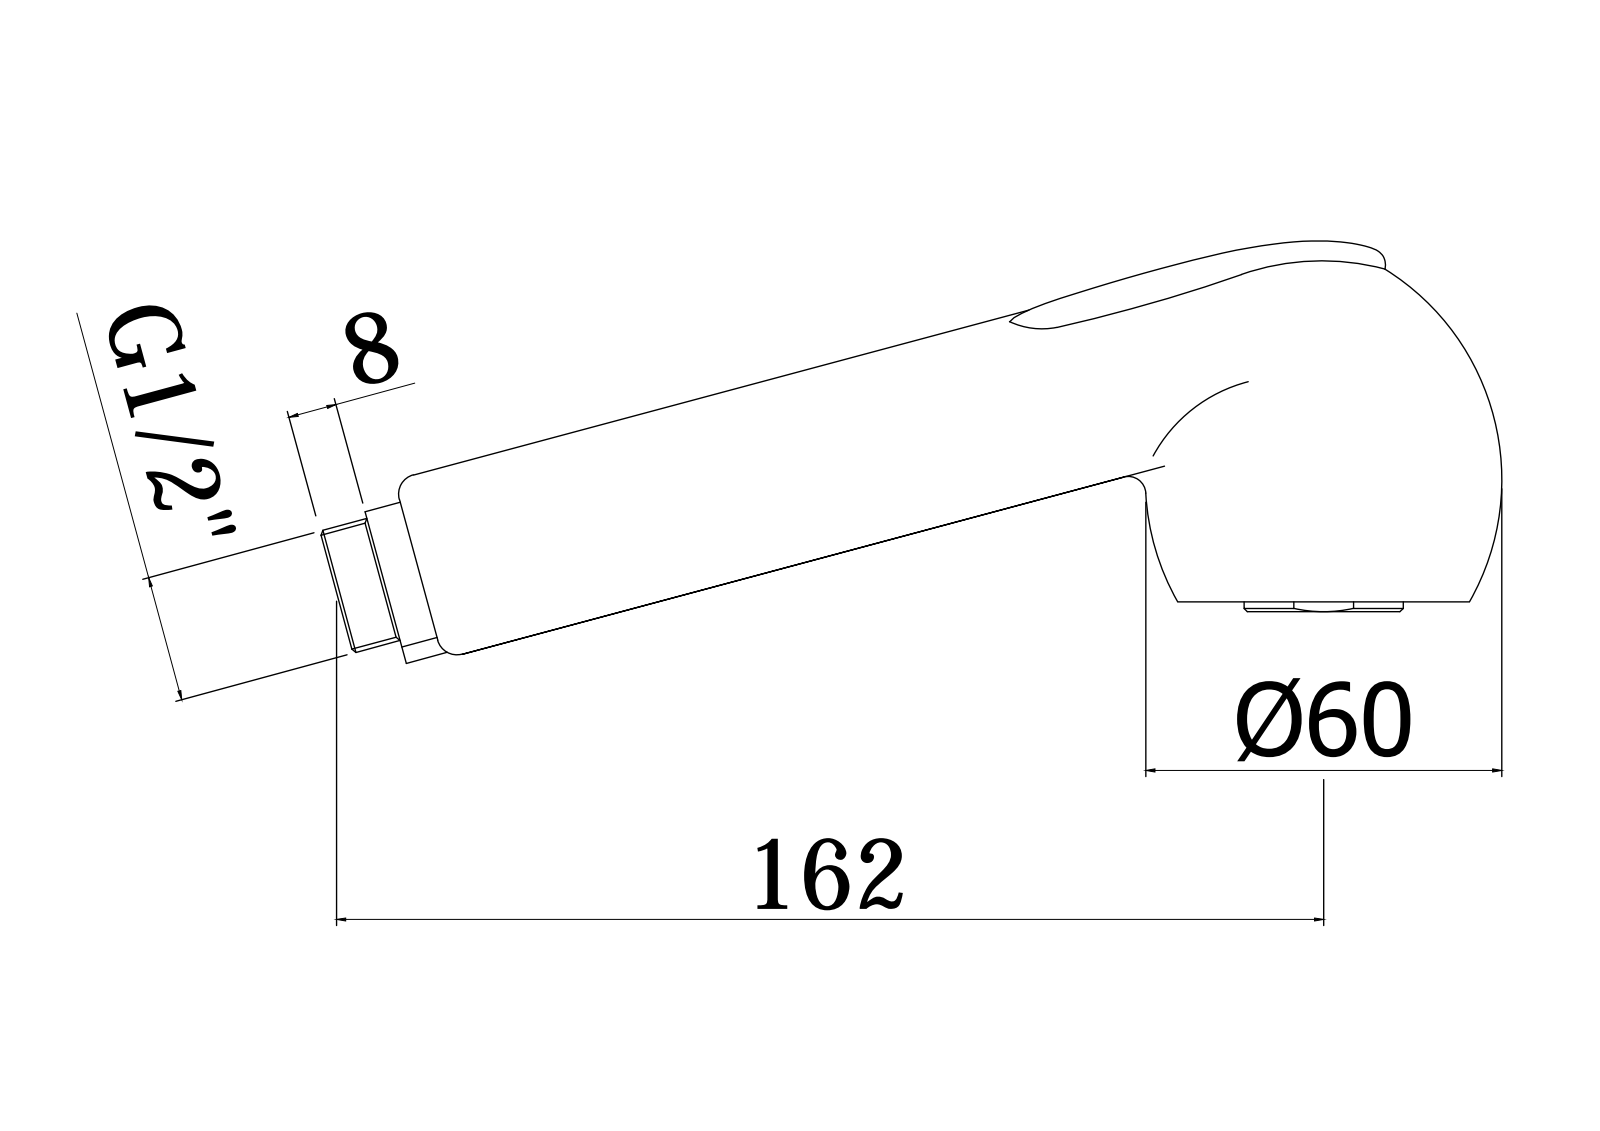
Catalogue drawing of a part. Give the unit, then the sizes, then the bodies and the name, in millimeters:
Units: millimetres
Overall size (bounding box): 189.58 × 60.7 × 56
Round holes (diameter × count): ⌀3.8 ×1, ⌀14.4 ×1, ⌀16 ×1, ⌀20 ×1, ⌀40 ×1
Round bosses / shafts (diameter × count): ⌀29.5 ×1, ⌀24 ×1, ⌀23 ×1, ⌀21 ×1, ⌀19.7 ×1, ⌀16.5 ×1, ⌀5 ×1
Partial cylindrical surfaces — rounded edges, fillets, slot ends (radius × count): R5.86 ×16, R8 ×2, R15 ×1, R50 ×1
Main face-to-face distances: 0.5, 5, 56, 51, 1, 6, 14.99, 11, 2, 45
Volume: 193 854 mm³ · Surface area: 29 546 mm²
Bodies: 1 solid, 184 faces (86 planar, 68 cylindrical, 30 other)
Part name (STEP PRODUCT): ZDOC002CR
STEP written by: CREO PARAMETRIC BY PTC INC, 2020044 (CONFIG_CONTROL_DESIGN)
